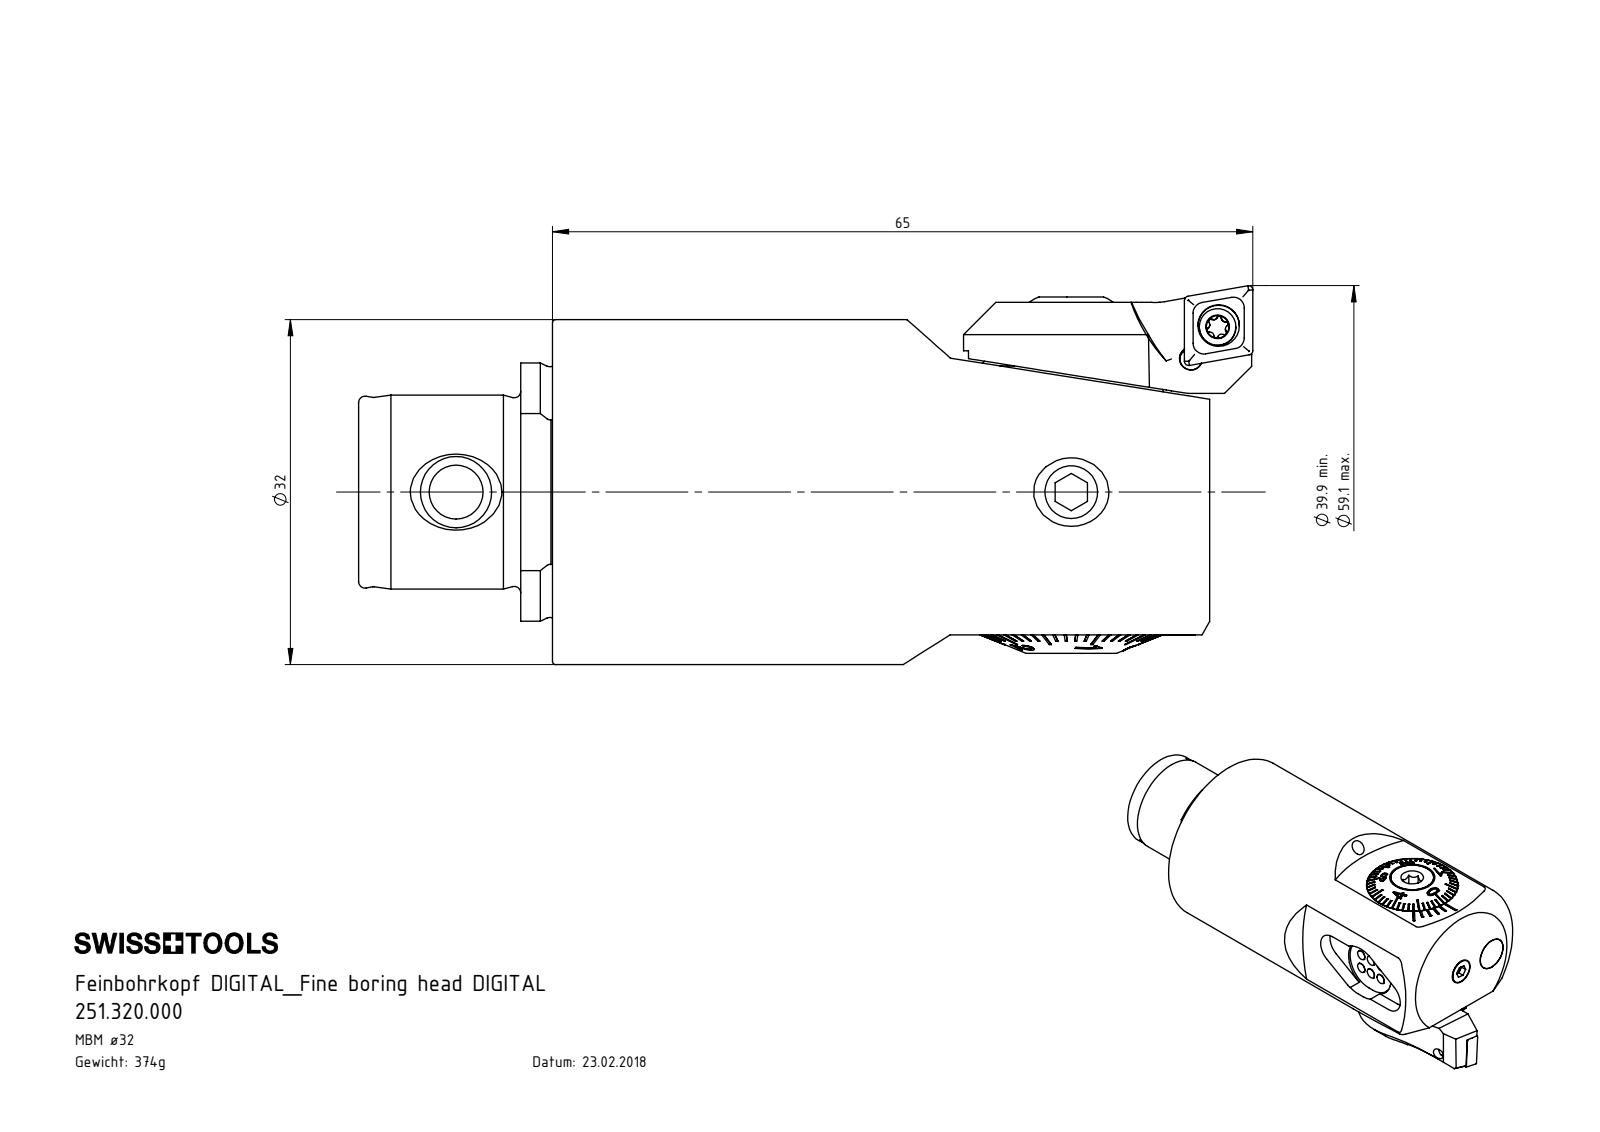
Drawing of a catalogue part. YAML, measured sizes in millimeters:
part_name: "251.320.000; PEE-DA1.011.026_A; Klebstoff D6; ISO 4026 - M6 x 5 (+8 more)"
step_written_by: "SolidWorks 2017 (CONFIG_CONTROL_DESIGN)"
units: millimeters
bodies: {solids: 20, faces: 912, planar: 395, cylindrical: 196, other: 321}
overall_size: [83, 35.15, 32]
volume: 48007
surface_area: 19954
round_holes:
  - {diameter: 2.5, count: 5}
  - {diameter: 5, count: 3}
  - {diameter: 2.05, count: 2}
  - {diameter: 8.5, count: 2}
  - {diameter: 0.7, count: 1}
  - {diameter: 2.1, count: 1}
  - {diameter: 2.7, count: 1}
  - {diameter: 2.8, count: 1}
  - {diameter: 2.9, count: 1}
  - {diameter: 3, count: 1}
  - {diameter: 3.85, count: 1}
  - {diameter: 6, count: 1}
round_bosses_or_shafts:
  - {diameter: 1.9, count: 6}
  - {diameter: 6, count: 2}
  - {diameter: 2.5, count: 2}
  - {diameter: 32, count: 1}
  - {diameter: 18, count: 1}
  - {diameter: 16.98, count: 1}
  - {diameter: 16.85, count: 1}
  - {diameter: 14.65, count: 1}
partial_cylinders:
  - {radius: 0.21, count: 6}
  - {radius: 0.36, count: 5}
  - {radius: 0.5, count: 4}
  - {radius: 1.1, count: 3}
  - {radius: 1.2, count: 3}
  - {radius: 1.75, count: 2}
  - {radius: 2.6, count: 2}
  - {radius: 3.1, count: 2}
face_to_face_distances: [4.5, 25.35, 20.85, 61, 5.5, 1.5, 3.7, 0.8, 1, 24.55]
hole_center_spacings: [57.1, 2.6, 2.84, 3.84, 3.99, 5.7, 8, 11.68]
